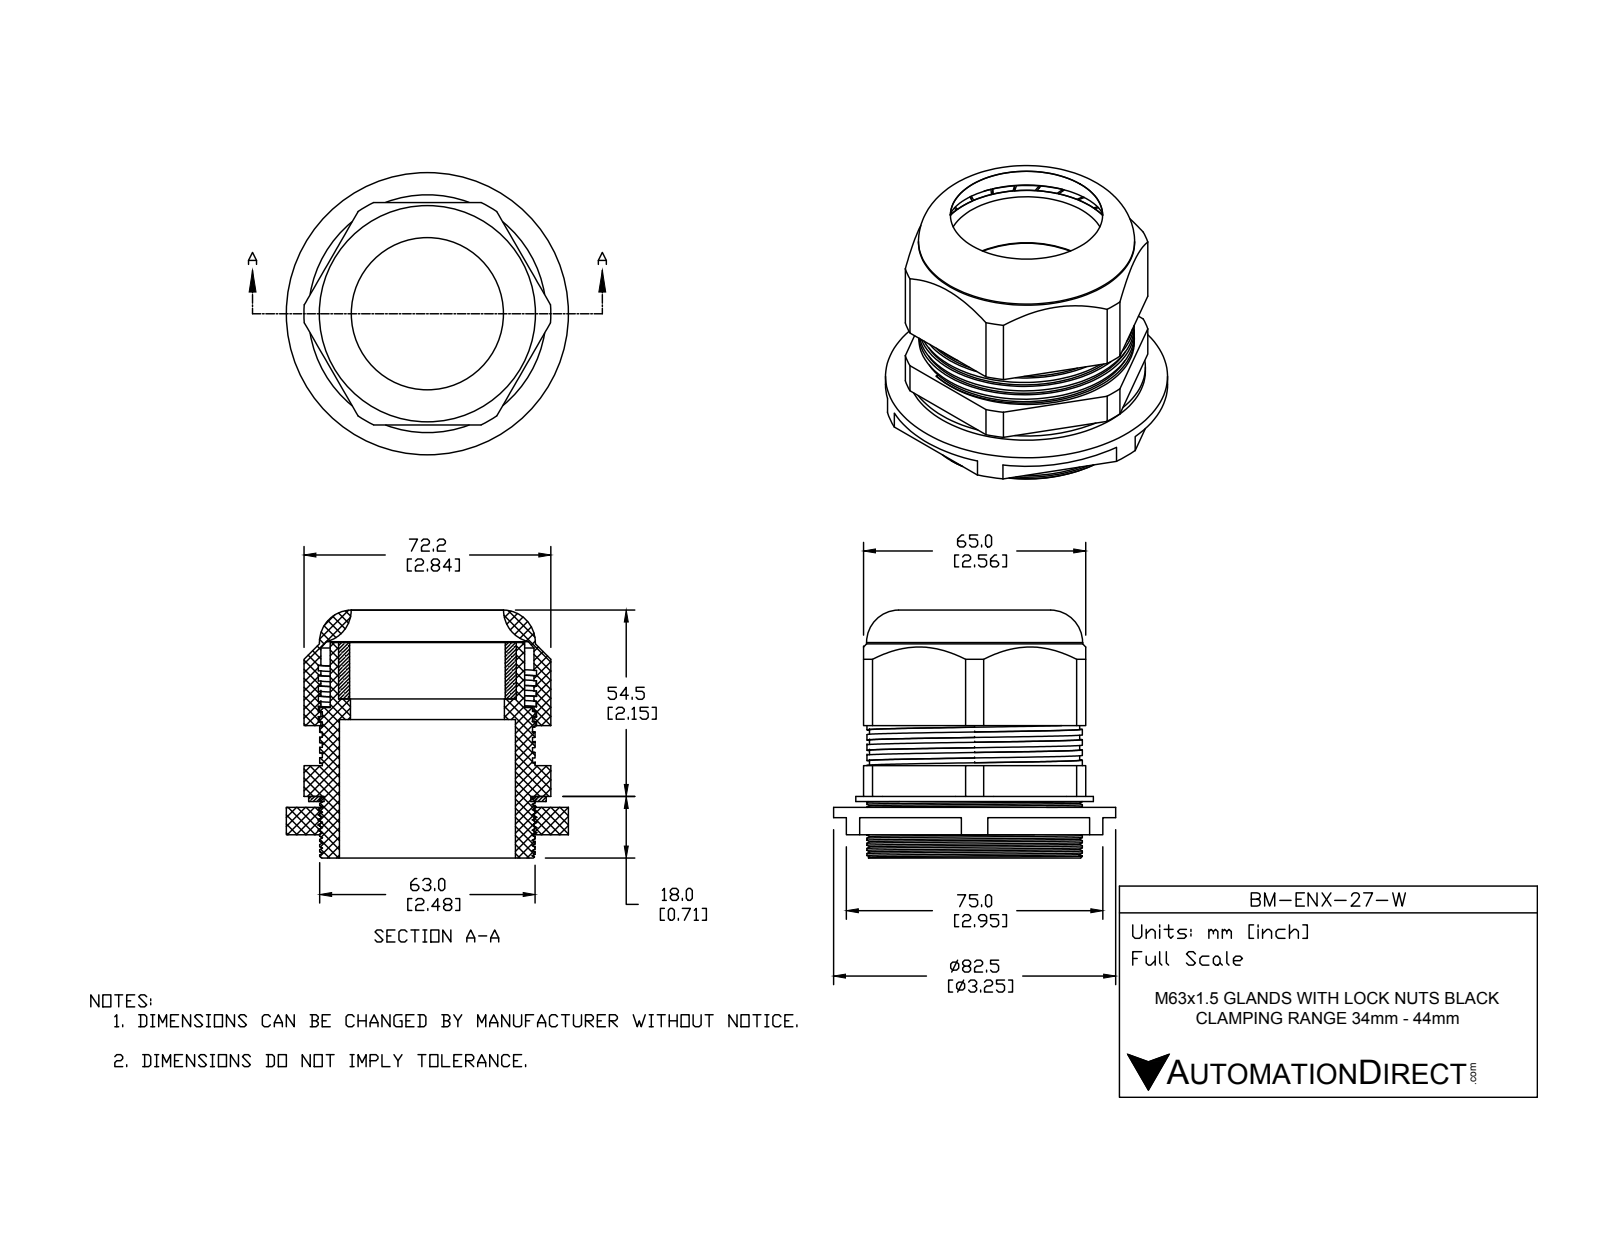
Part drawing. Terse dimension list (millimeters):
name: BM-ENX-27-W
written by: SolidWorks 2015 (CONFIG_CONTROL_DESIGN)
unit: mm
bodies: 5 solids, 309 faces (139 planar, 149 cylindrical, 21 other)
size: 82.5 × 82.5 × 72.5
volume: 103 908 mm³; area: 67 209 mm²
holes: 1× ⌀44.5, 1× ⌀45, 1× ⌀45.5, 1× ⌀52, 1× ⌀60.5, 1× ⌀62.33
bosses: 1× ⌀82.5, 1× ⌀69.5, 1× ⌀63.2, 1× ⌀63, 1× ⌀56.9, 1× ⌀51.5
rounds: 1× R36.1
face distances: 65, 10.5, 2.5, 46.5, 16.5, 8, 5, 28.5, 9, 19.5
